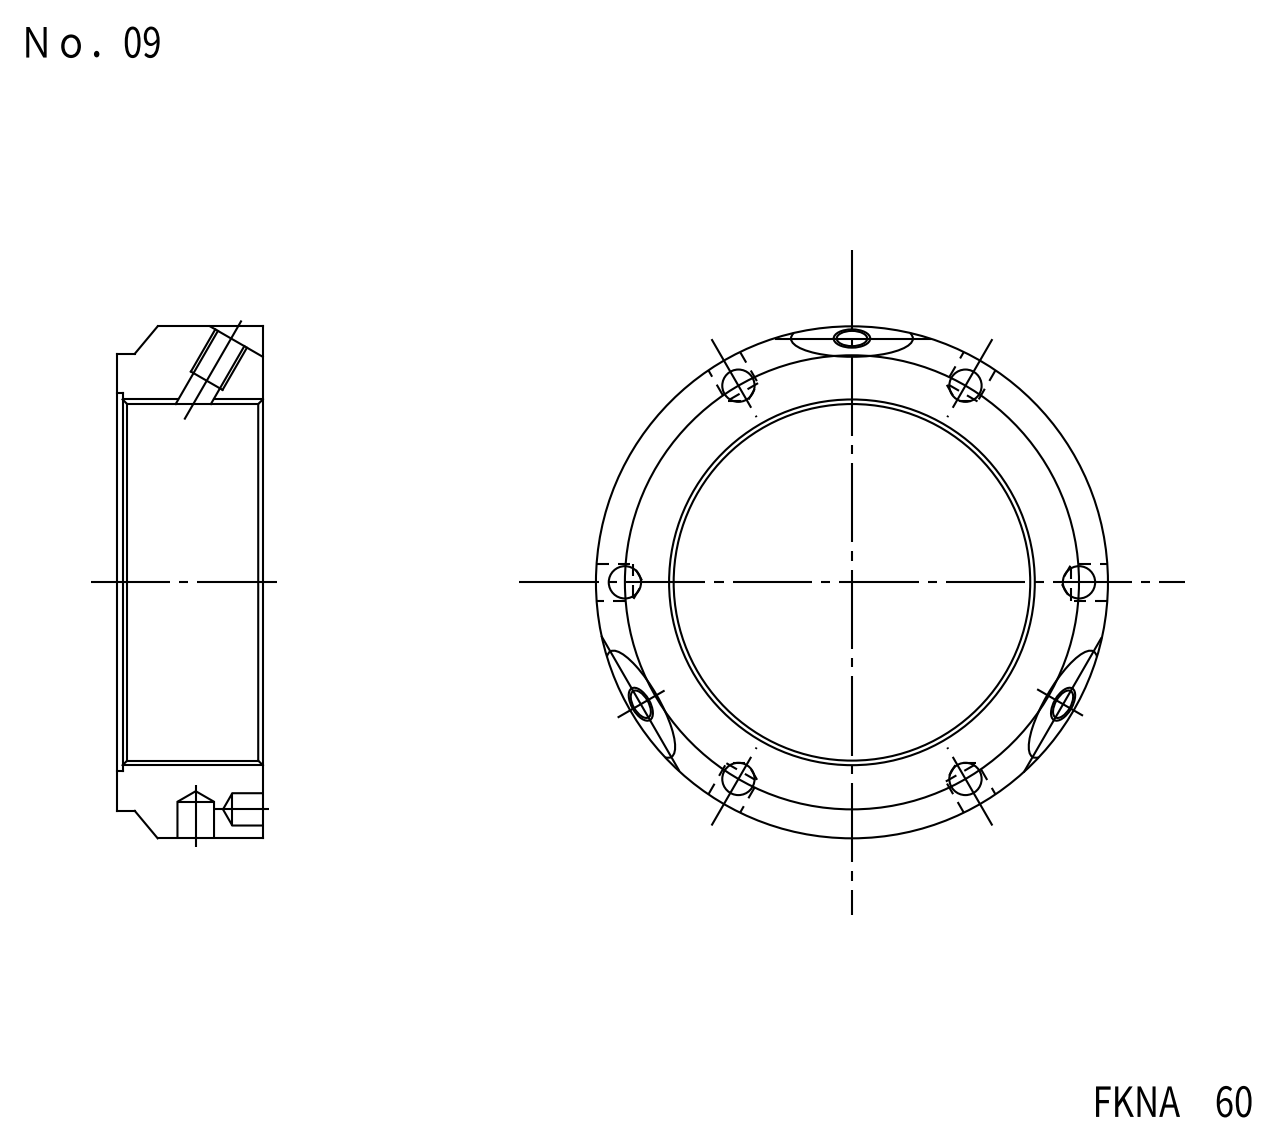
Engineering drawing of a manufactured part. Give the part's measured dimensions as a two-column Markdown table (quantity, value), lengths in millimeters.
| quantity | value |
| --- | --- |
| part name | FKD FKNA60 |
| STEP written by | Autodesk Inventor LT (CONFIG_CONTROL_DESIGN) |
| units | millimeters |
| bodies | 1 solid, 44 faces (6 planar, 25 cylindrical, 13 other) |
| overall size | 84 × 84 × 24 |
| volume | 59 243 mm³ |
| surface area | 17 331 mm² |
| round holes (diameter × count) | 5.3 × 6, 6 × 3, 6.1 × 3, 4.92 × 2, 4.92 × 1, 60 × 1, 62 × 1 |
| round bosses / shafts (diameter × count) | 84 × 1, 75 × 1 |
| partial cylindrical surfaces (radius × count) | 20 × 3 |
| main face-to-face distances | 24, 1.5, 22.5 |
| hole center spacings | 37.25, 64.52, 74.5, 37.26, 64.51, 74.51 |
